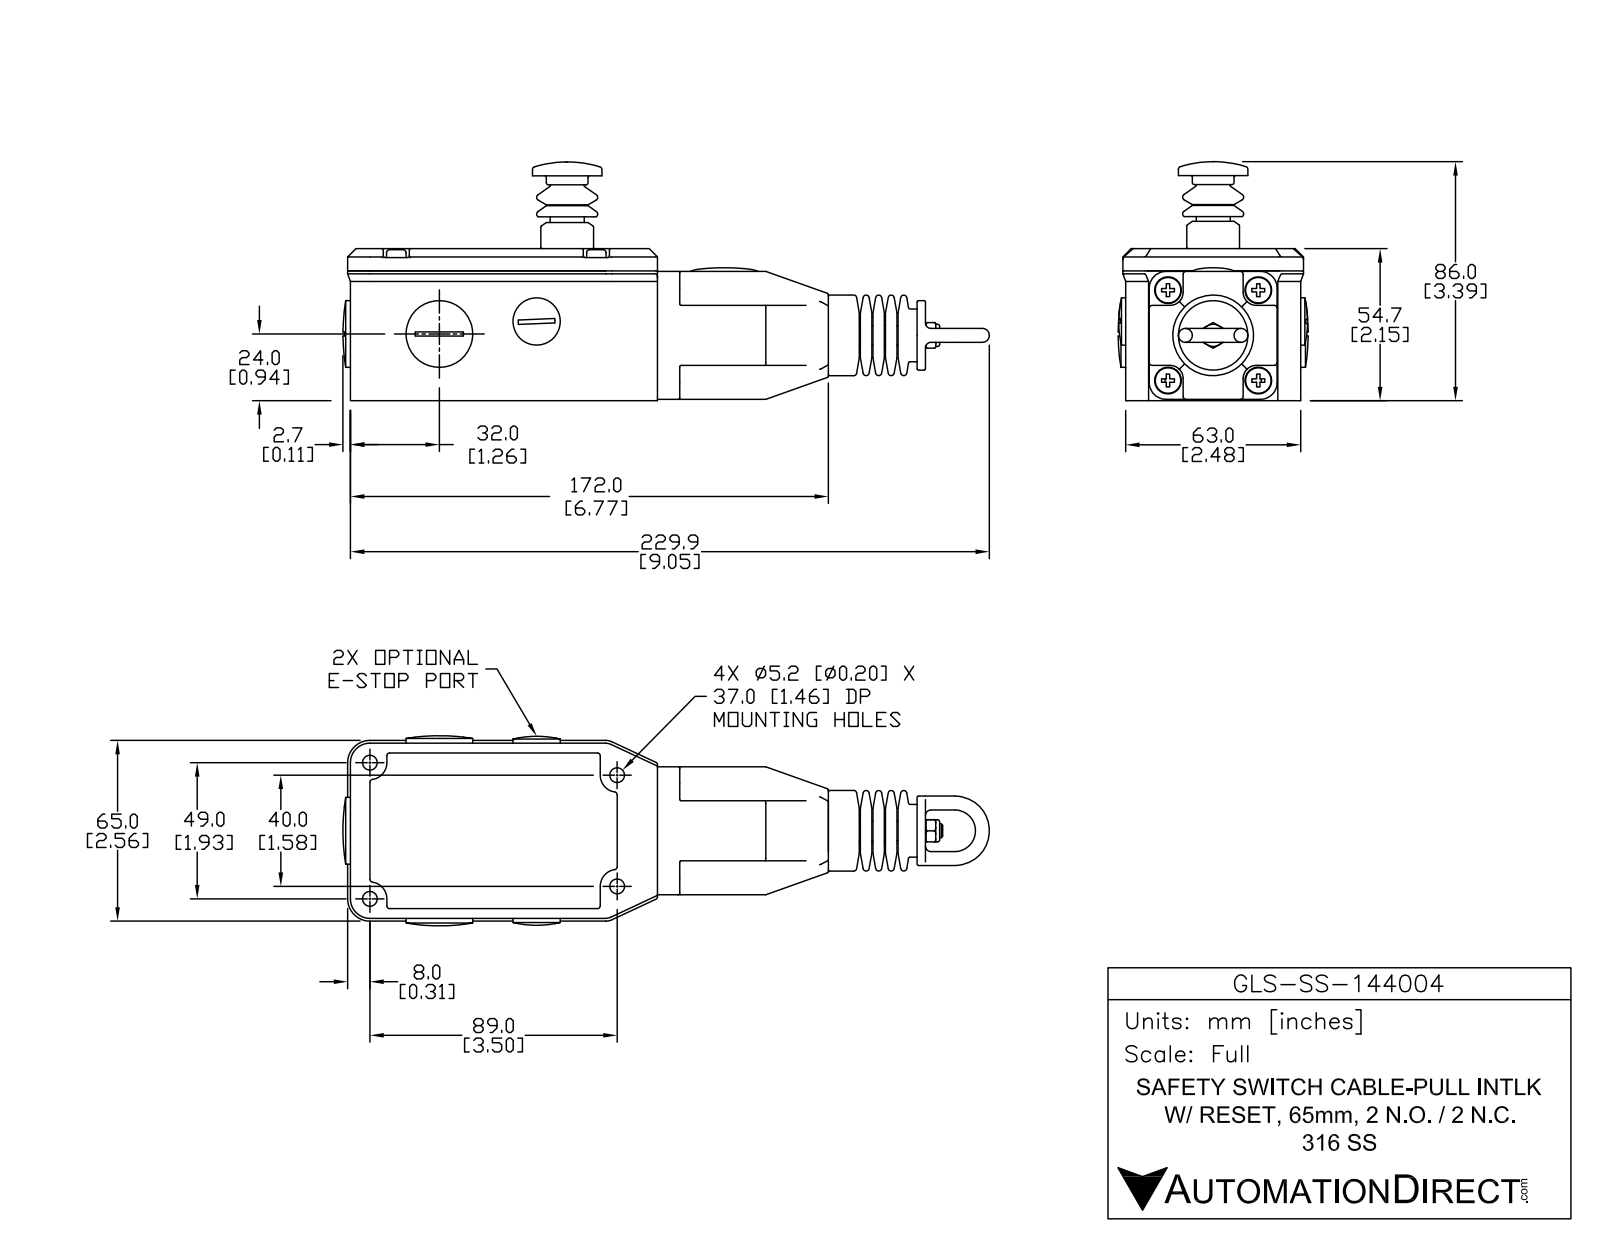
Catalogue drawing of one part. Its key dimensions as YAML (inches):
part_name: "GLS-SS-144004"
step_written_by: "SolidWorks 2013 (AUTOMOTIVE_DESIGN)"
units: inches
bodies: {solids: 1, faces: 654, planar: 196, cylindrical: 224, other: 234}
overall_size: [9.205, 3.386, 3.055]
volume: 30.35
surface_area: 86.84
round_holes:
  - {diameter: 0.205, count: 4}
  - {diameter: 0.374, count: 4}
round_bosses_or_shafts:
  - {diameter: 0.362, count: 4}
  - {diameter: 0.236, count: 4}
  - {diameter: 1.055, count: 2}
  - {diameter: 0.984, count: 2}
  - {diameter: 0.748, count: 2}
  - {diameter: 0.197, count: 2}
  - {diameter: 1.142, count: 1}
  - {diameter: 0.669, count: 1}
partial_cylinders:
  - {radius: 0.02, count: 74}
  - {radius: 0.03, count: 20}
  - {radius: 0.039, count: 8}
  - {radius: 0.118, count: 4}
  - {radius: 0.177, count: 4}
  - {radius: 0.189, count: 4}
  - {radius: 0.197, count: 4}
  - {radius: 0.63, count: 4}
face_to_face_distances: [2.142, 2.559, 2.154, 0.461, 1.311, 1.772, 0.177, 2.205, 0.354, 1.976]
hole_center_spacings: [1.276, 1.283, 1.809, 3.508, 3.918, 1.575, 1.929]
